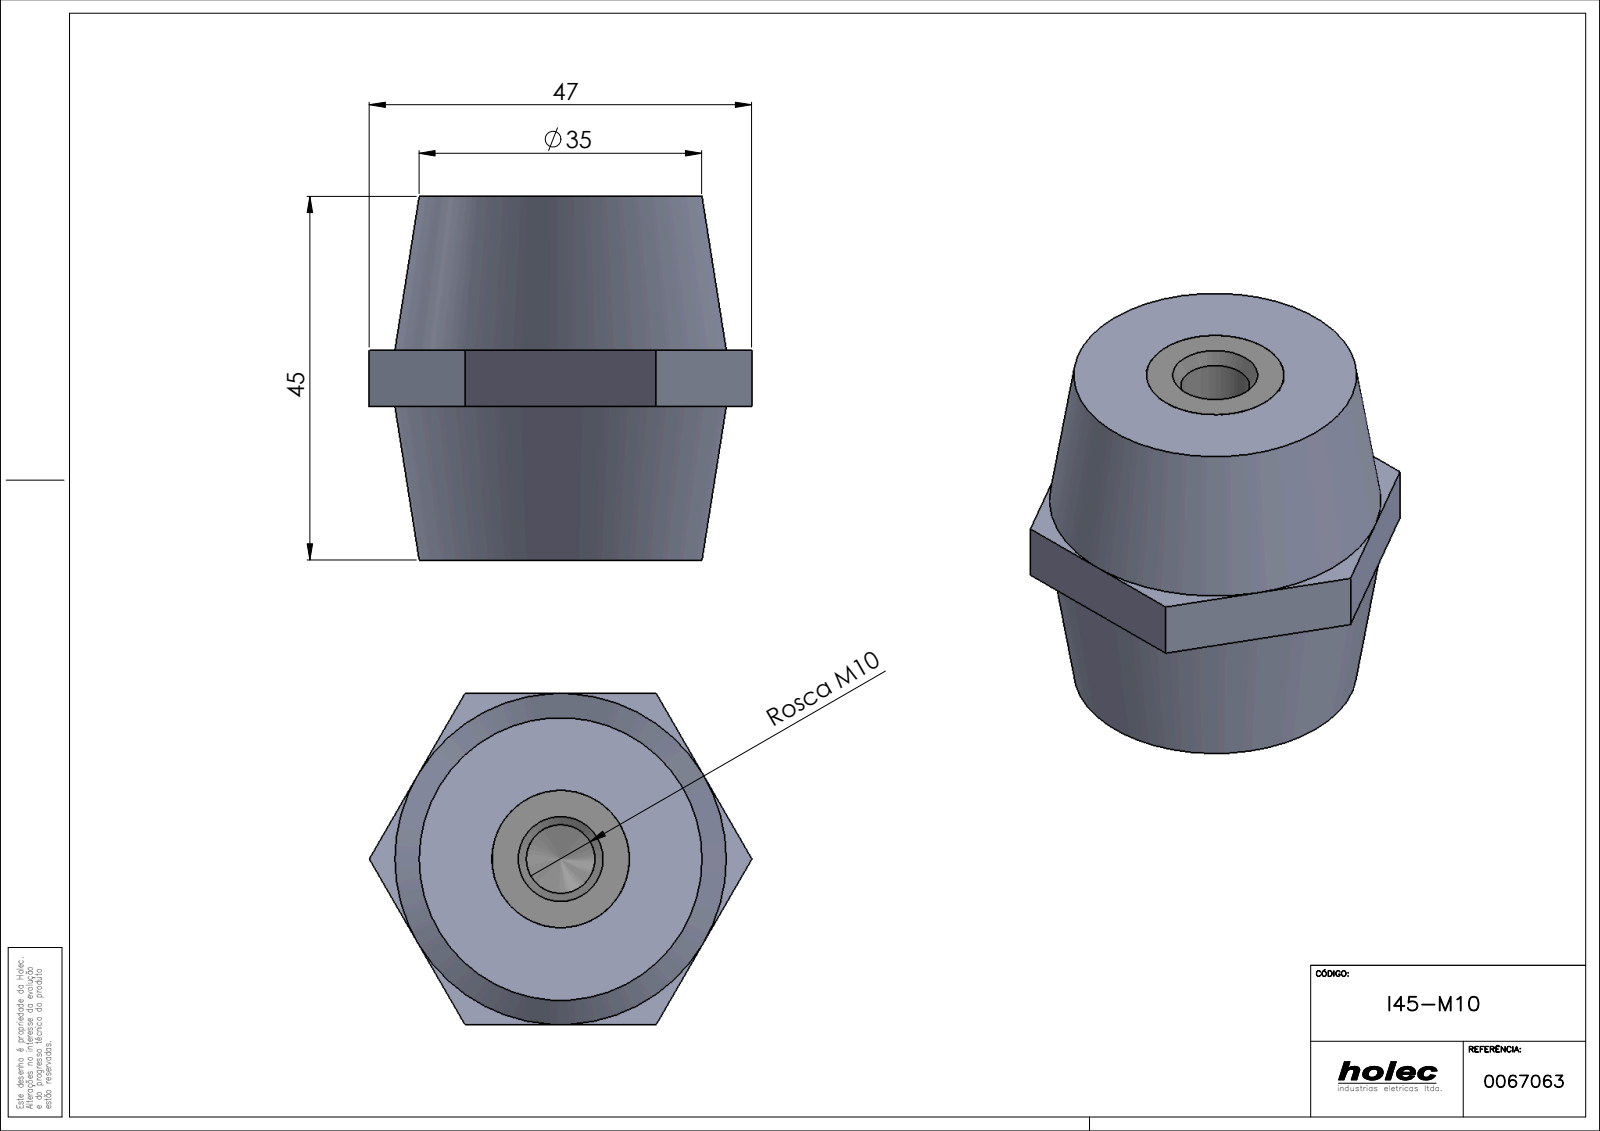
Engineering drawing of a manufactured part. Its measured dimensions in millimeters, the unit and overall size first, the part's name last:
Units: millimetres
Overall size (bounding box): 47.34 × 45 × 41
Round holes (diameter × count): ⌀8.5 ×1, ⌀14 ×1
Main face-to-face distances: 12, 17, 29, 45, 28.01, 7, 28, 5, 41, 16.99
Volume: 51 656 mm³ · Surface area: 13 828 mm²
Bodies: 3 solids, 162 faces (82 planar, 12 cylindrical, 68 other)
Part name (STEP PRODUCT): PB1_0002; I45-M10; PB1_0105(PB1_0105_10)
STEP written by: SolidWorks 2017 (AUTOMOTIVE_DESIGN)
